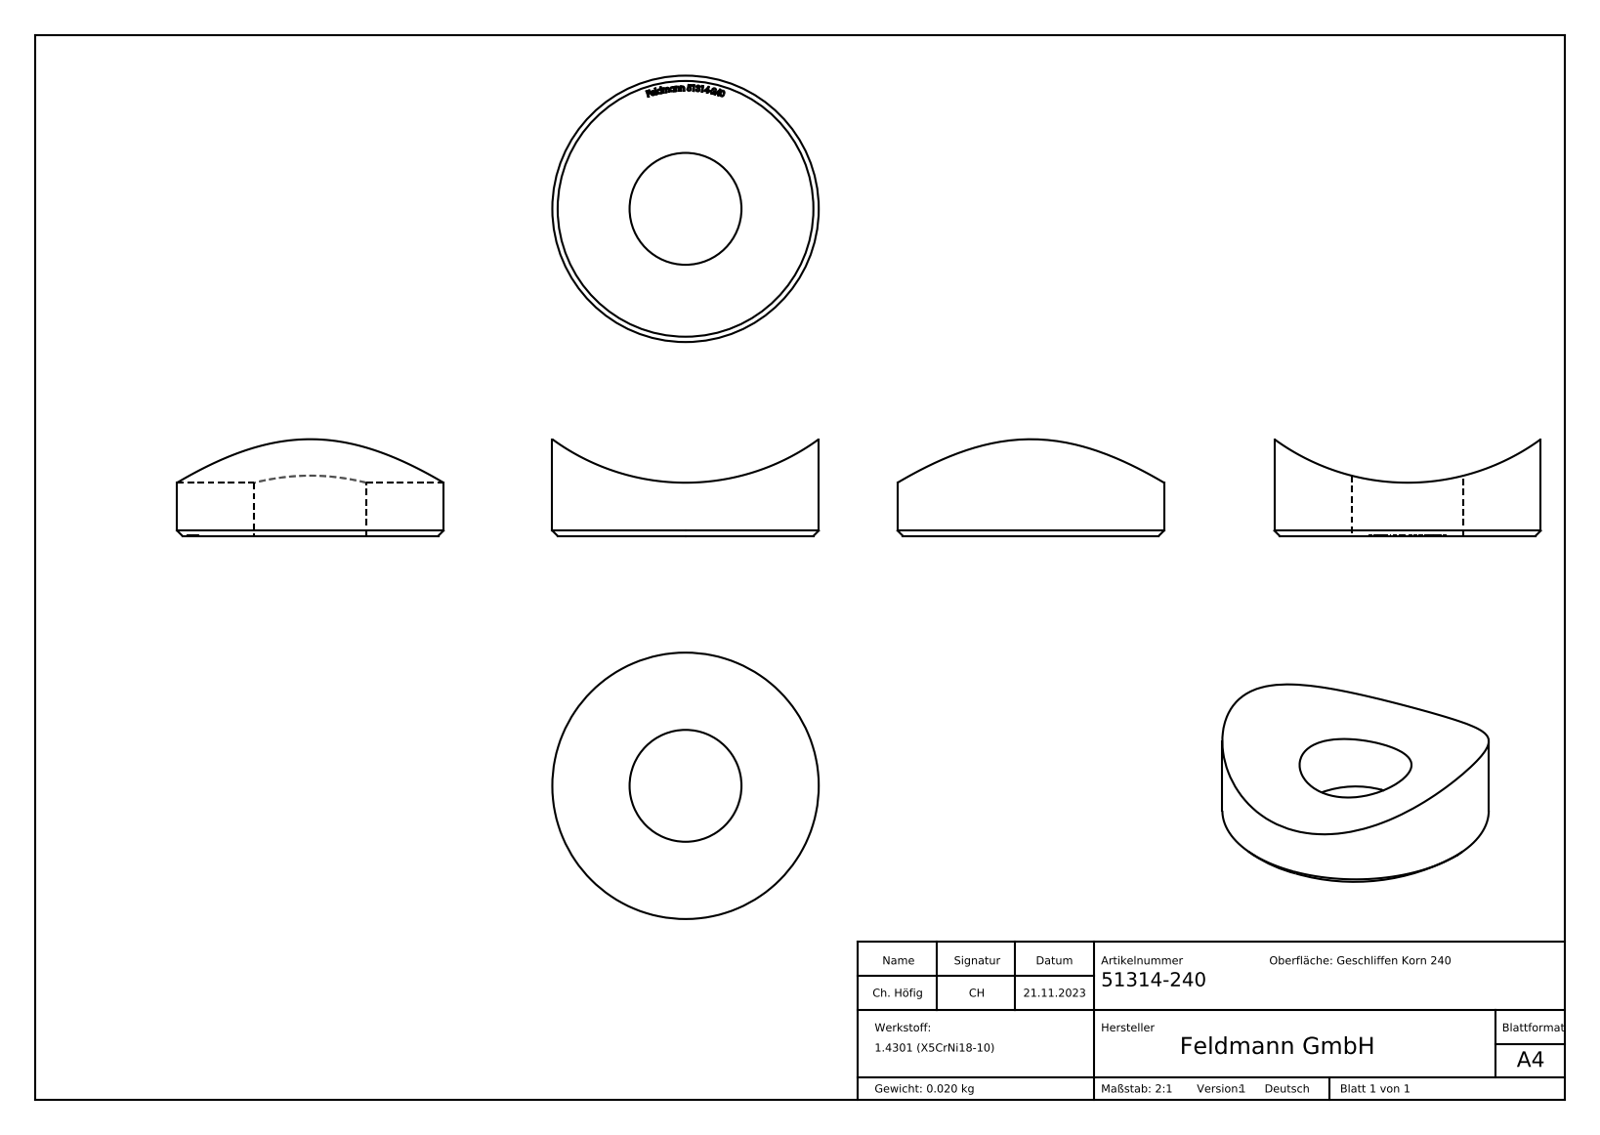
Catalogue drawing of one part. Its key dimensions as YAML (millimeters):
part_name: "51314-240"
step_written_by: "SolidWorks 2018 (CONFIG_CONTROL_DESIGN)"
units: millimeters
bodies: {solids: 1, faces: 224, planar: 135, cylindrical: 3, other: 86}
overall_size: [25, 25, 9.08]
volume: 2471
surface_area: 1537
round_holes:
  - {diameter: 10.5, count: 1}
round_bosses_or_shafts:
  - {diameter: 25, count: 1}
partial_cylinders:
  - {radius: 21.2, count: 1}
face_to_face_distances: [0.54, 0.49, 0.59, 0.34, 0.32, 0.39, 0.48, 0.36, 0.31, 0.55]
